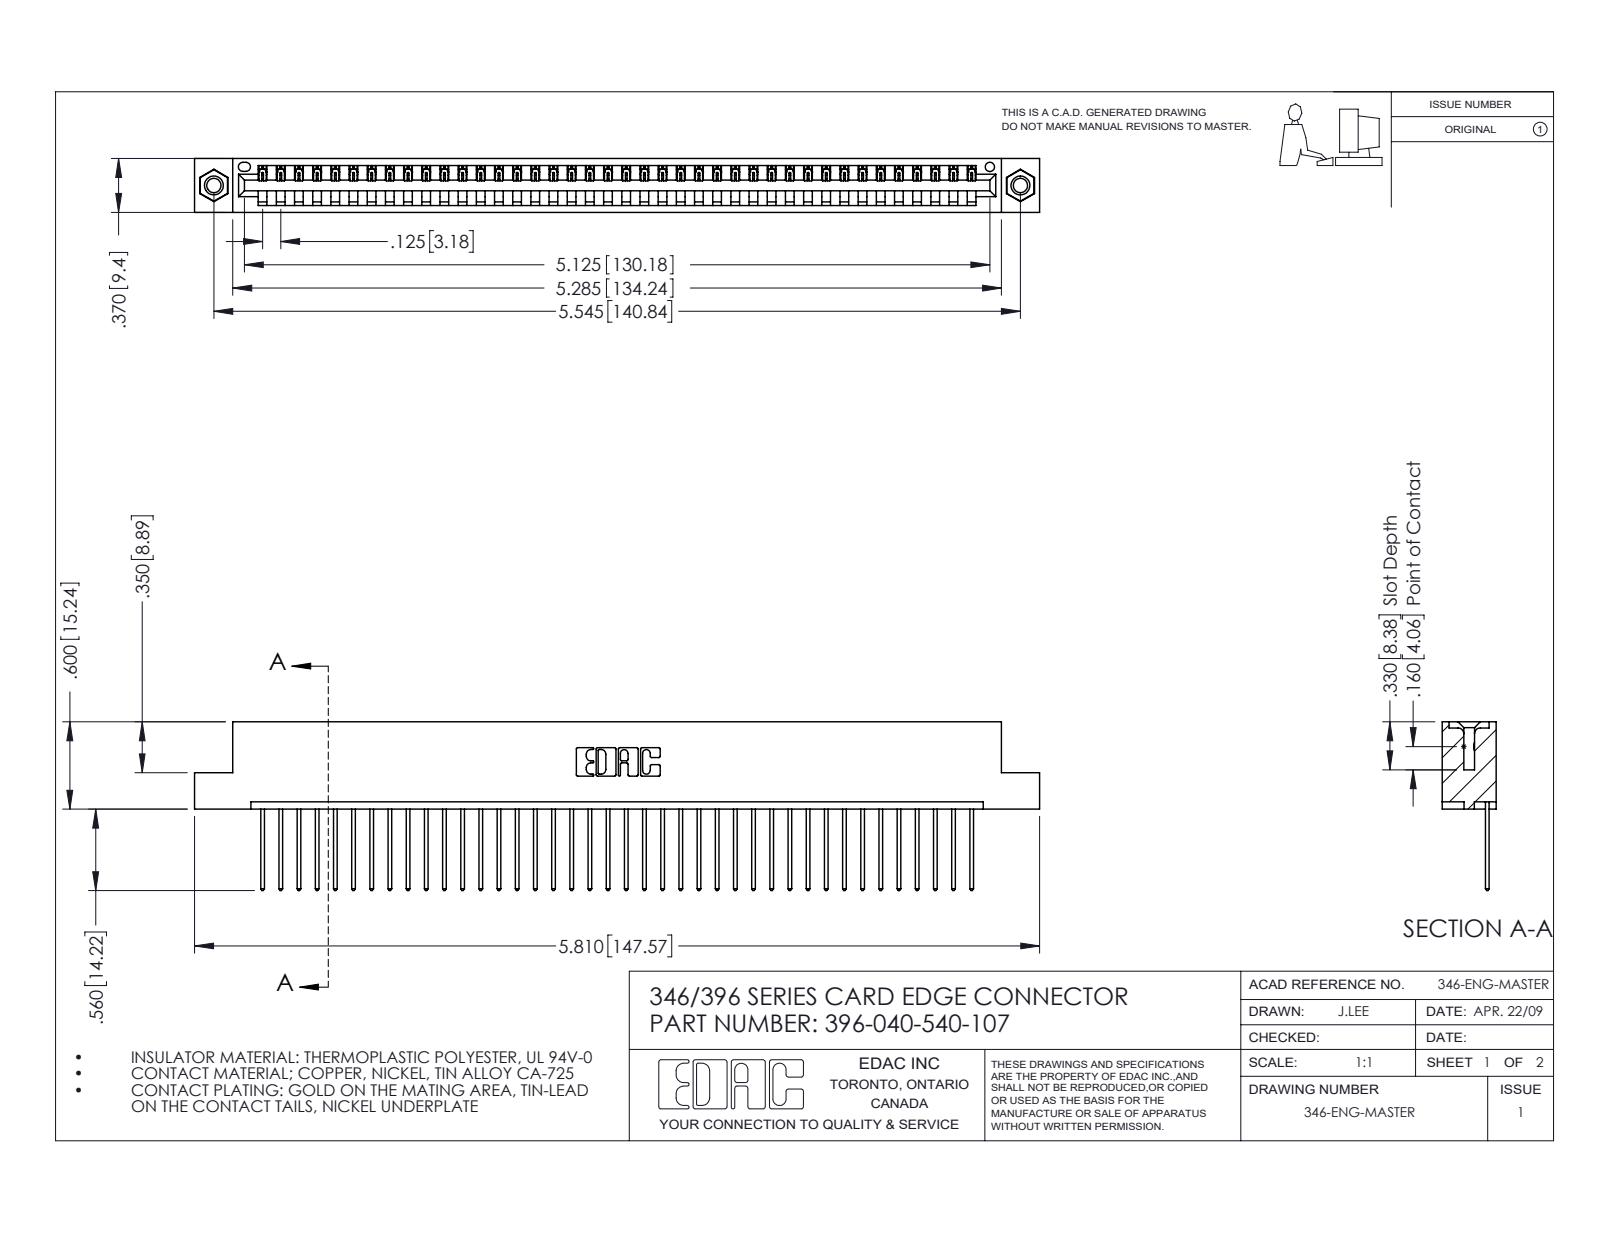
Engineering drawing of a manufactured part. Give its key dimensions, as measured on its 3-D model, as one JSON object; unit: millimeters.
{"part_name": "345-292-001_345-293-140; 345-250-001_345-250-005-103; 396-040-540-107; 346 Part_Flush Mounting Lugs - 0.156 Dia-TI", "step_written_by": "SolidWorks 2016 (CONFIG_CONTROL_DESIGN)", "units": "millimeters", "bodies": {"solids": 43, "faces": 2502, "planar": 1708, "cylindrical": 778, "other": 16}, "overall_size": [147.6, 29.5, 9.4], "volume_mm3": 14200, "surface_area_mm2": 18100, "round_holes": [[2.5, 2], [3.2, 2], [4, 2], [1.6, 1]], "round_bosses_or_shafts": [[3.9, 2]], "partial_cylinders_radius": [[0.2, 80], [0.3, 80], [0.3, 22], [0.2, 6], [0.8, 6], [0.7, 3], [0.8, 2], [1, 2]], "face_to_face_distances": [1.2, 8.2, 9.4, 6.4, 1.8, 7.6, 0.6, 3.8, 5.6, 2.5], "hole_center_spacings": [6.2, 135.5, 140.8]}
